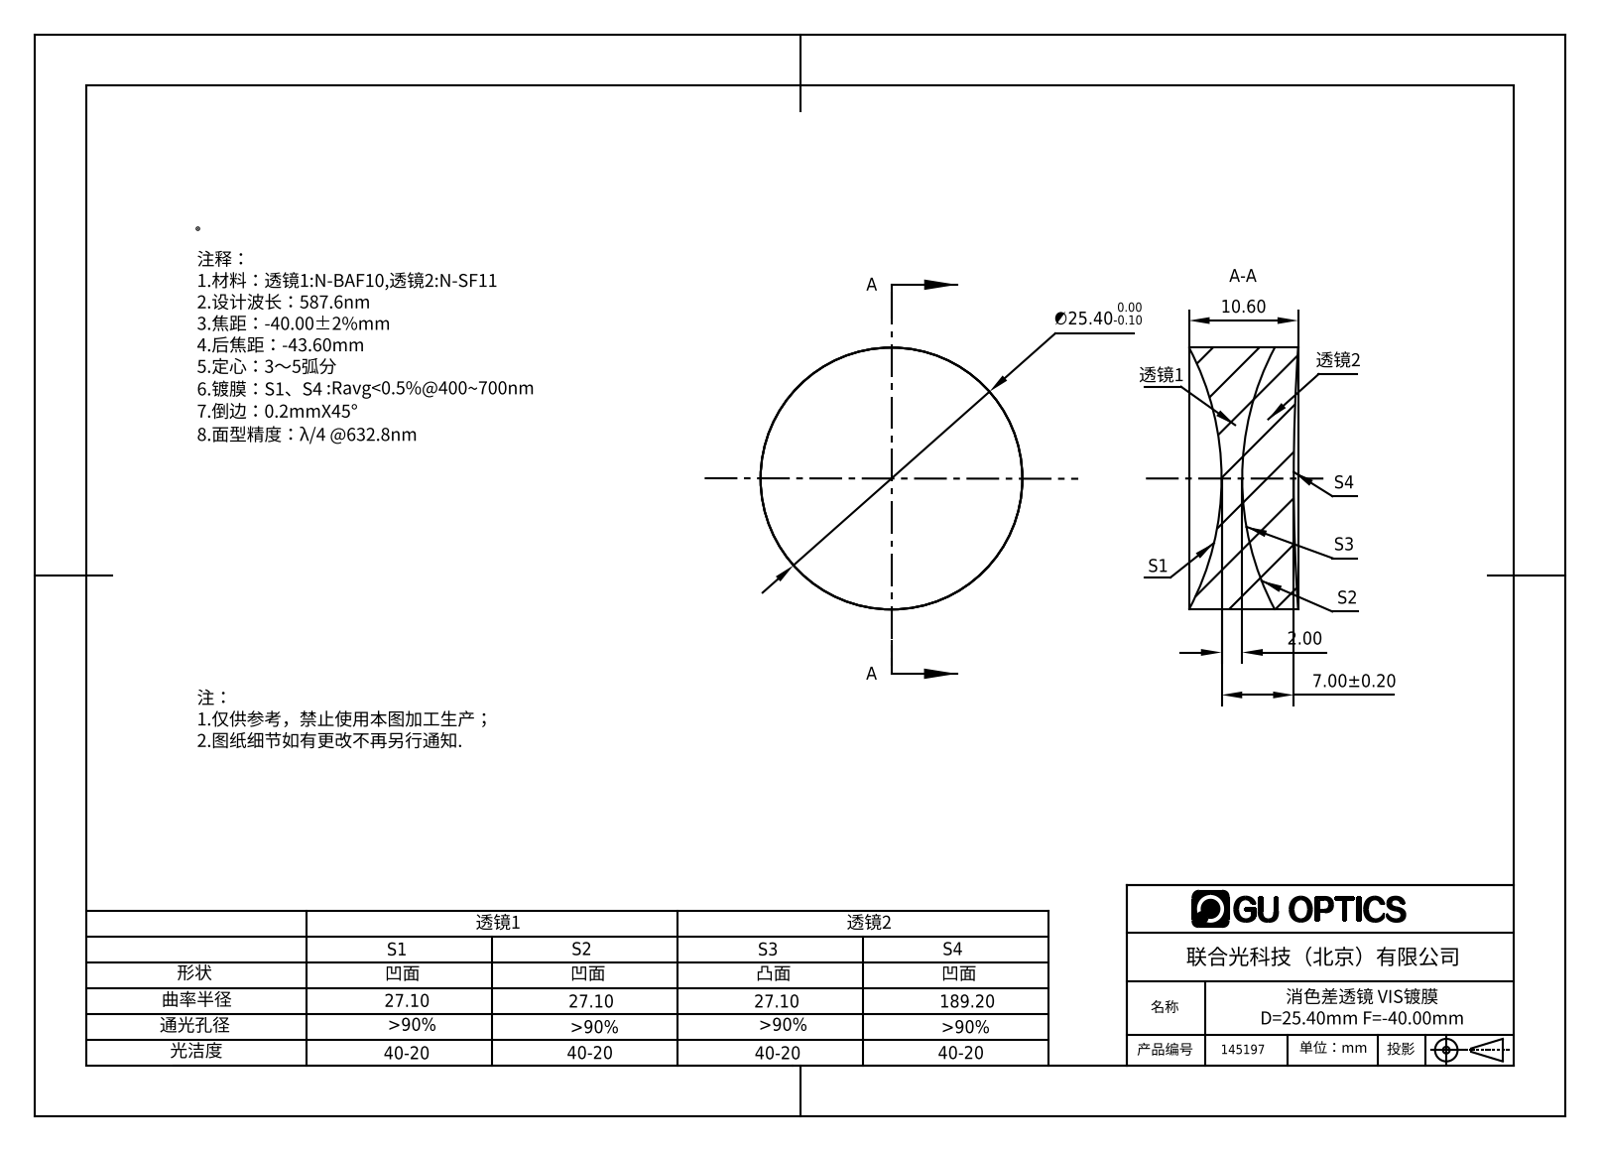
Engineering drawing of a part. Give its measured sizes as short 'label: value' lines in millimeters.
name: 145197
written by: SolidWorks 2016 (AUTOMOTIVE_DESIGN)
unit: mm
bodies: 2 solids, 12 faces (0 planar, 4 cylindrical, 8 other)
size: 25.4 × 25.4 × 10.59
volume: 4 439 mm³; area: 2 966 mm²
bosses: 1× ⌀25.4
